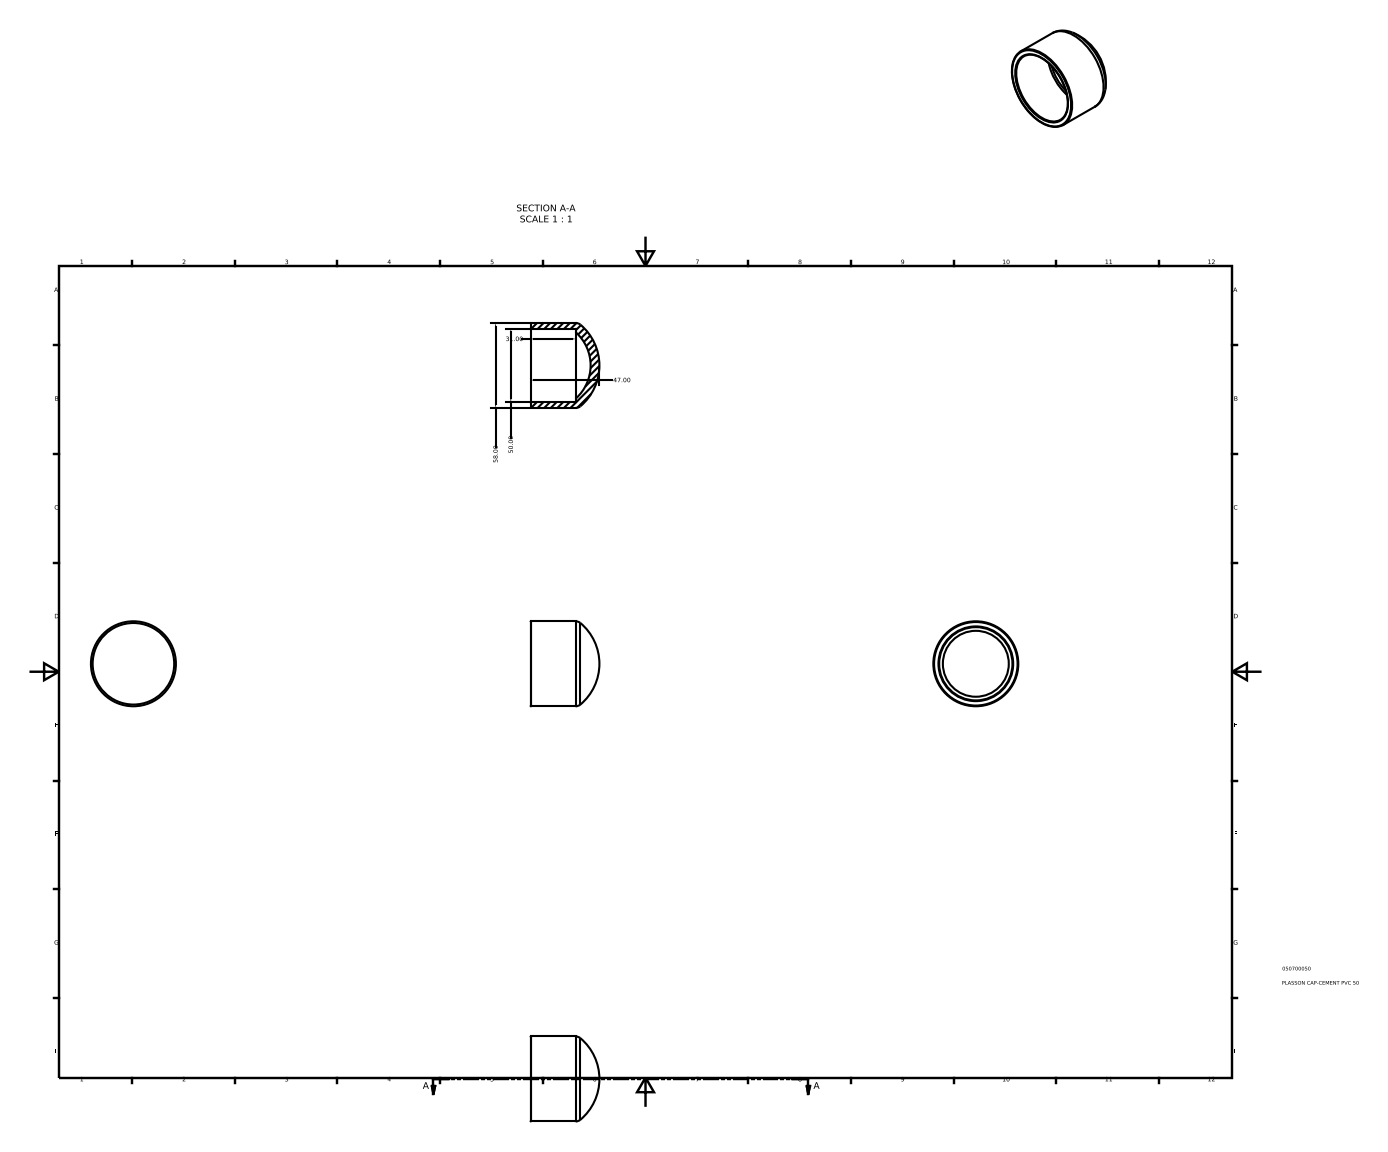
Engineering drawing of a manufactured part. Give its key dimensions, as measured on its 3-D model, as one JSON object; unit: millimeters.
{"part_name": "050700050", "step_written_by": "Autodesk Inventor 2015 (AUTOMOTIVE_DESIGN)", "units": "millimeters", "bodies": {"solids": 1, "faces": 9, "planar": 2, "cylindrical": 2, "other": 5}, "overall_size": [58, 58, 47], "volume_mm3": 37247, "surface_area_mm2": 16955, "round_holes": [[50, 1]], "round_bosses_or_shafts": [[58, 1]], "face_to_face_distances": [31]}
